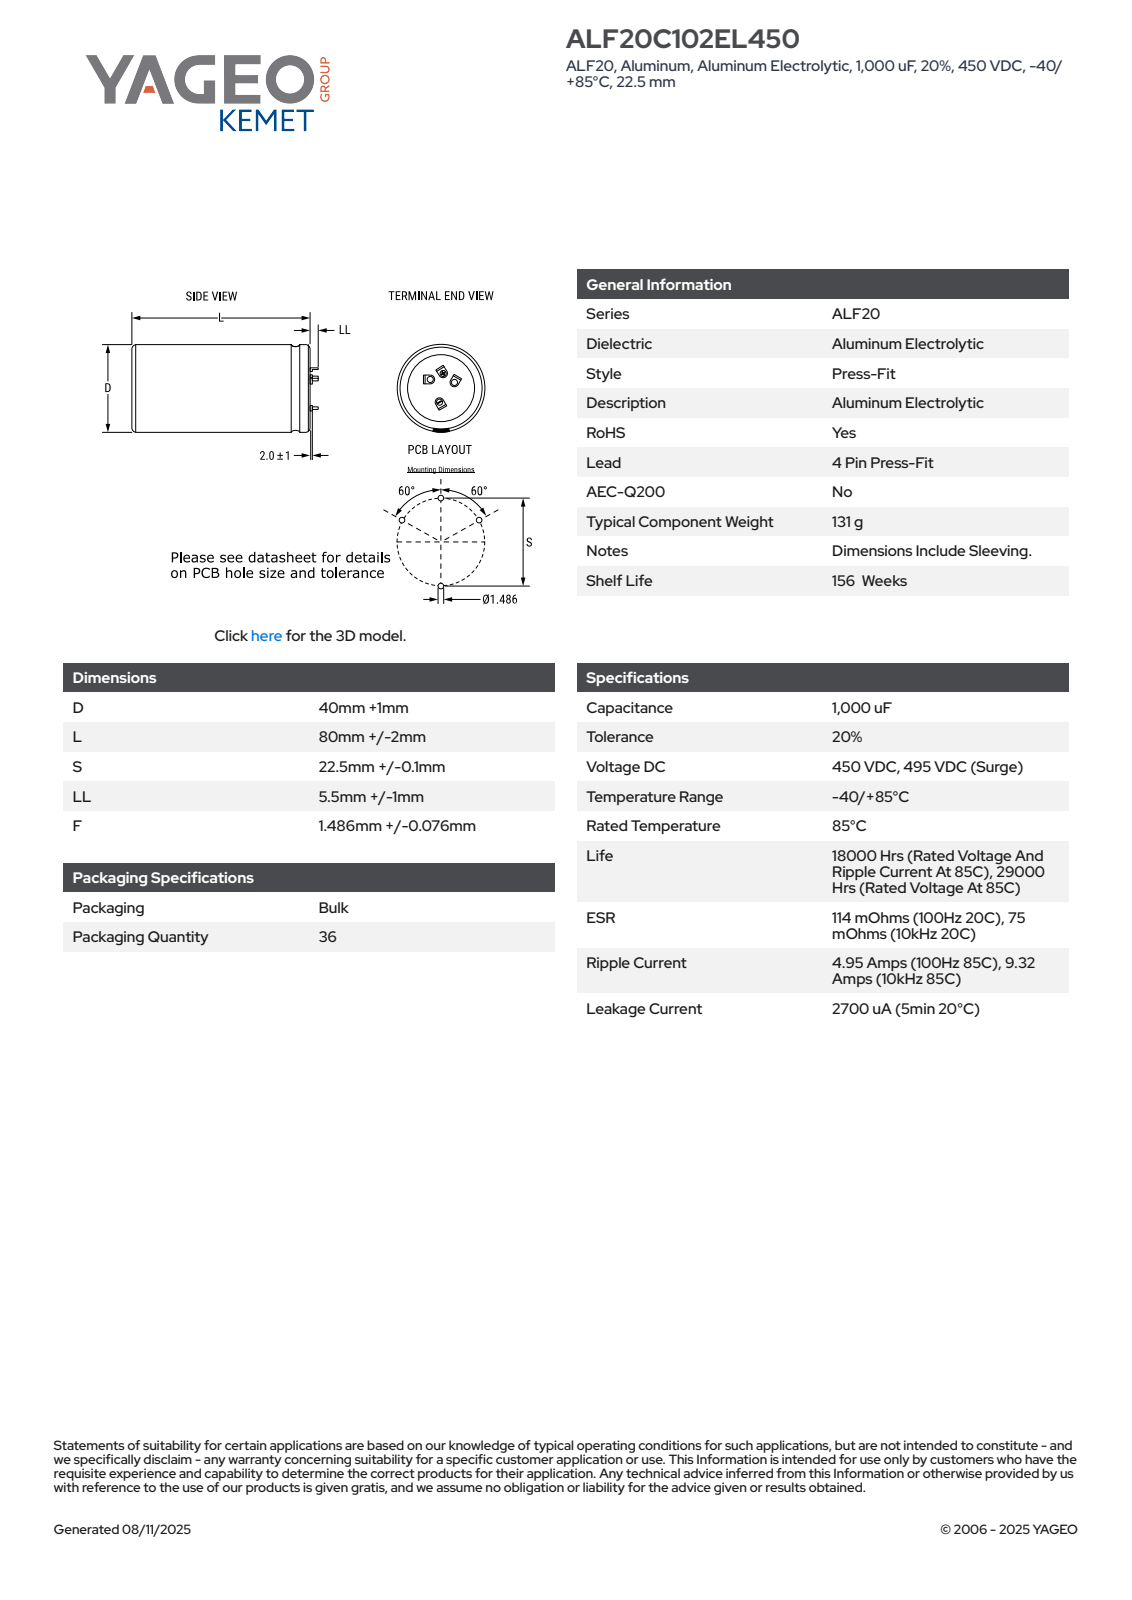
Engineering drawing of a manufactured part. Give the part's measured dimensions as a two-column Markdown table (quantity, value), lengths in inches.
| quantity | value |
| --- | --- |
| part name | CARS_ALF2040C_40X80_D41L82S22.5LL6.5 |
| STEP written by | SolidWorks 2014 (AUTOMOTIVE_DESIGN) |
| units | inches |
| bodies | 6 solids, 333 faces (139 planar, 138 cylindrical, 56 other) |
| overall size | 3.489 × 1.614 × 1.614 |
| volume | 6.591 in³ |
| surface area | 20.92 in² |
| round bosses / shafts (diameter × count) | 0.138 × 4, 1.614 × 1 |
| partial cylindrical surfaces (radius × count) | 0.006 × 50, 0.004 × 8, 0.017 × 8, 0.098 × 3, 0.099 × 1 |
| main face-to-face distances | 3.228, 3.229, 0.031, 3.229, 0.197, 0.118, 0.119, 3.347, 3.347, 0.197 |
